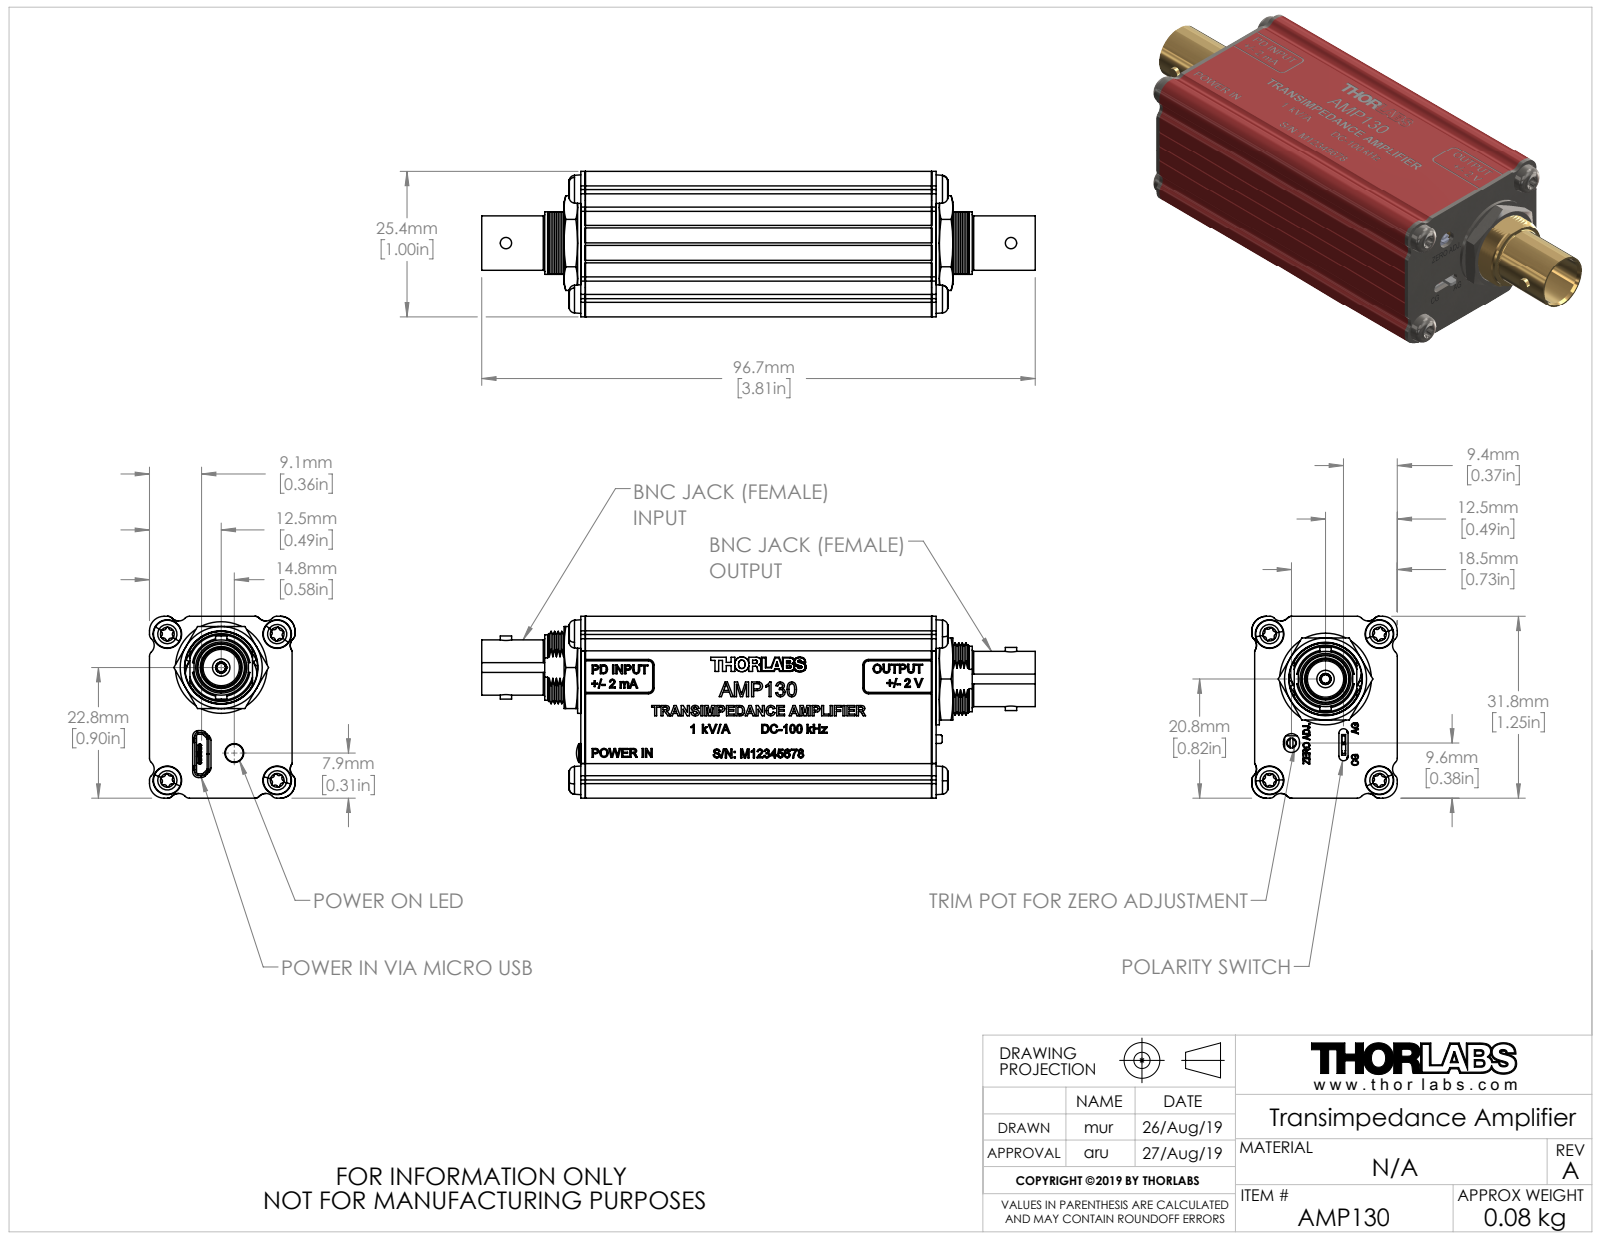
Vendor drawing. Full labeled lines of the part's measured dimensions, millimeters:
Part name (STEP PRODUCT): 19.10.23_AMP130 WEB
STEP written by: SolidWorks 2018 (AUTOMOTIVE_DESIGN)
Units: millimetres
Bodies: 0 solids, 4455 faces (2779 planar, 694 cylindrical, 982 other)
Overall size (bounding box): 96.65 × 31.75 × 25.41
Round holes (diameter × count): ⌀3.5 ×6, ⌀0.2 ×4, ⌀0.6 ×4, ⌀0.85 ×2, ⌀0.9 ×2, ⌀1.19 ×2, ⌀1.49 ×2, ⌀1.93 ×2, ⌀4.04 ×2, ⌀6.93 ×2, ⌀8.86 ×2, ⌀12.7 ×2
Round bosses / shafts (diameter × count): ⌀0.46 ×6, ⌀2.5 ×4, ⌀2.22 ×4, ⌀16 ×2, ⌀11.43 ×2, ⌀10.46 ×2, ⌀9.65 ×2, ⌀6.91 ×2
Partial cylindrical surfaces — rounded edges, fillets, slot ends (radius × count): R0.24 ×43, R0.42 ×43, R1.02 ×26, R0.2 ×25, R0.15 ×20, R1.59 ×14, R0.25 ×12, R0.25 ×11
Main face-to-face distances: 1.27, 3.05, 1.64, 12, 0.8, 9.14, 61.25, 6.1, 12.19, 4.32
Hole centre spacings: 19.18, 1.11, 2, 4, 5.64, 7.03, 10.97, 11.08
